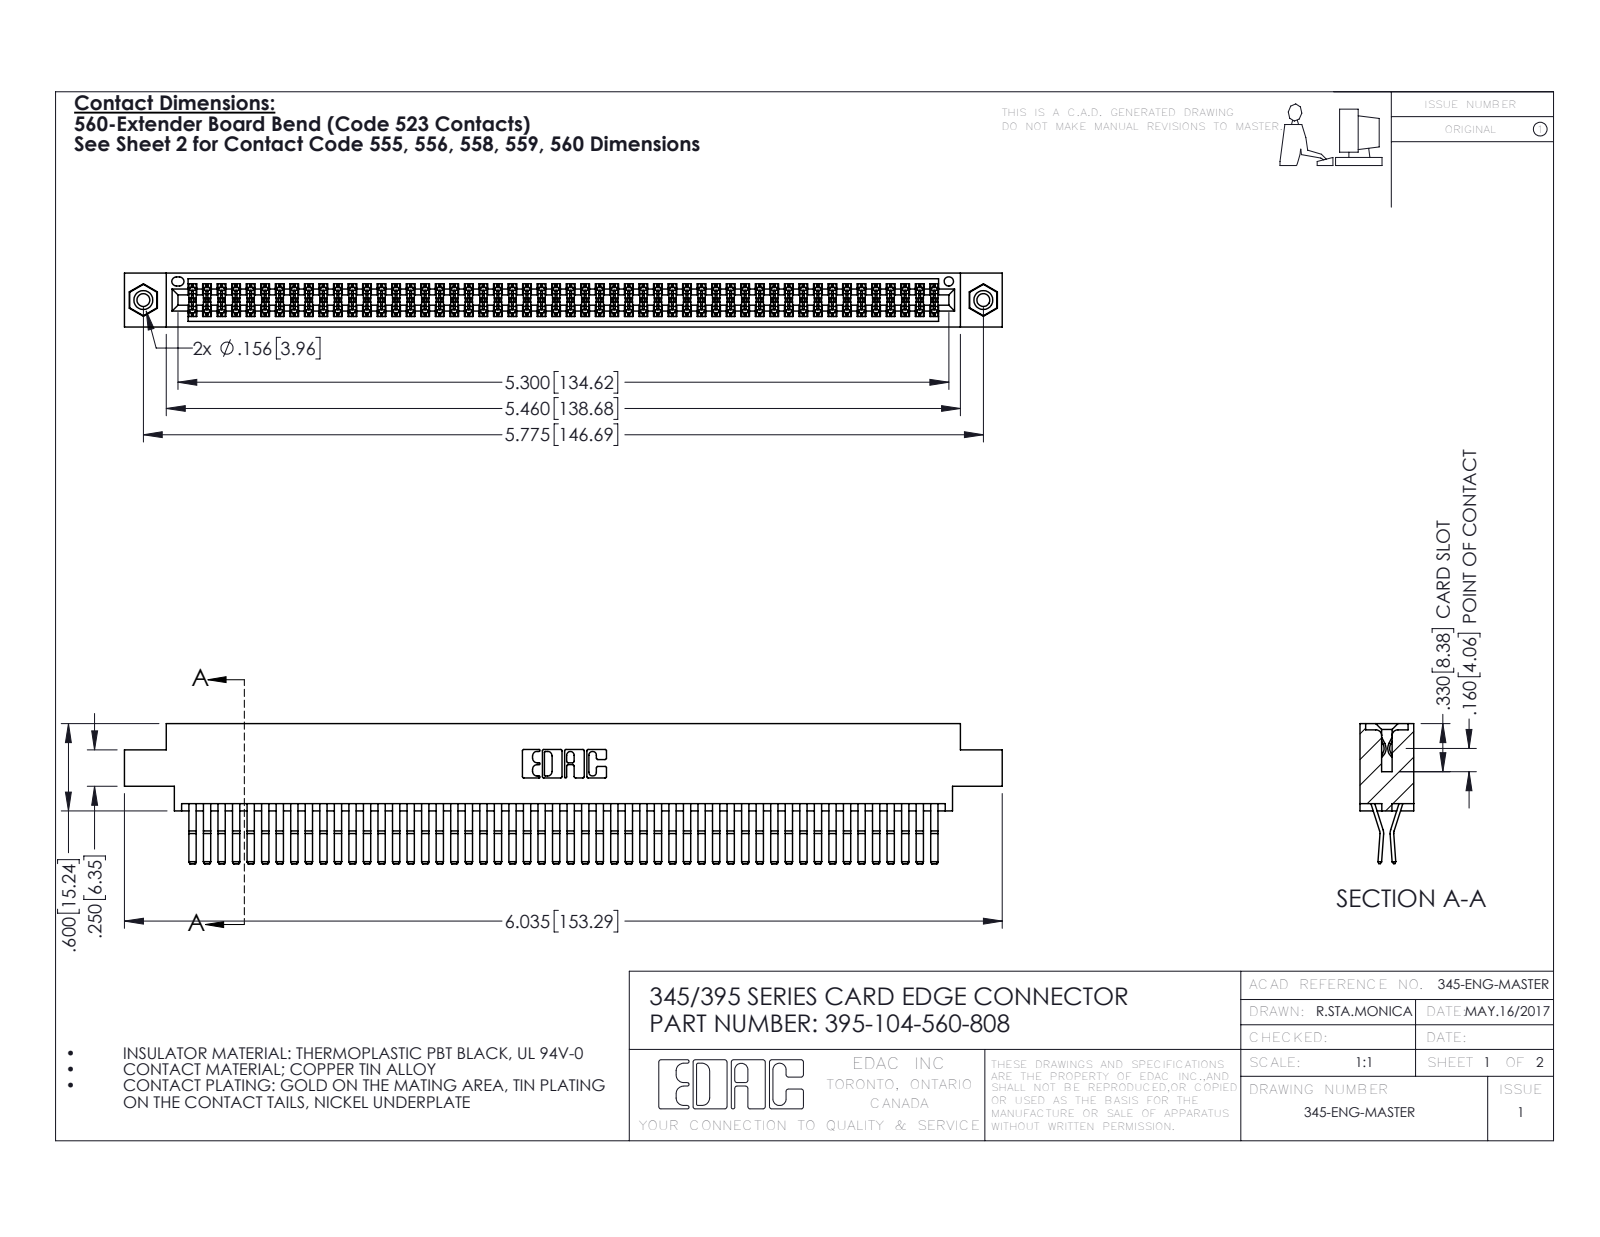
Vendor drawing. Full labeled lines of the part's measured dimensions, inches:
Part name (STEP PRODUCT): 395-104-560-808; 345-292-001_560 Tail; 345-250-001_345-250-003-102; 345 Part_0.170 Offset - 0.156 Dia-TI
STEP written by: SolidWorks 2016 (CONFIG_CONTROL_DESIGN)
Units: inches
Bodies: 107 solids, 5598 faces (3548 planar, 2034 cylindrical, 16 other)
Overall size (bounding box): 6.035 × 0.962 × 0.37
Volume: 0.949 in³ · Surface area: 38.88 in²
Round holes (diameter × count): ⌀0.089 ×2, ⌀0.125 ×2, ⌀0.156 ×2, ⌀0.064 ×1
Round bosses / shafts (diameter × count): ⌀0.155 ×2
Partial cylindrical surfaces — rounded edges, fillets, slot ends (radius × count): R0.006 ×157, R0.01 ×22, R0.007 ×6, R0.031 ×6, R0.026 ×3, R0.01 ×2, R0.014 ×2, R0.019 ×2
Main face-to-face distances: 0.025, 0.072, 0.298, 0.37, 0.2, 0.098, 0.272, 0.225, 0.175, 0.149
Hole centre spacings: 0.27, 5.539, 5.775
